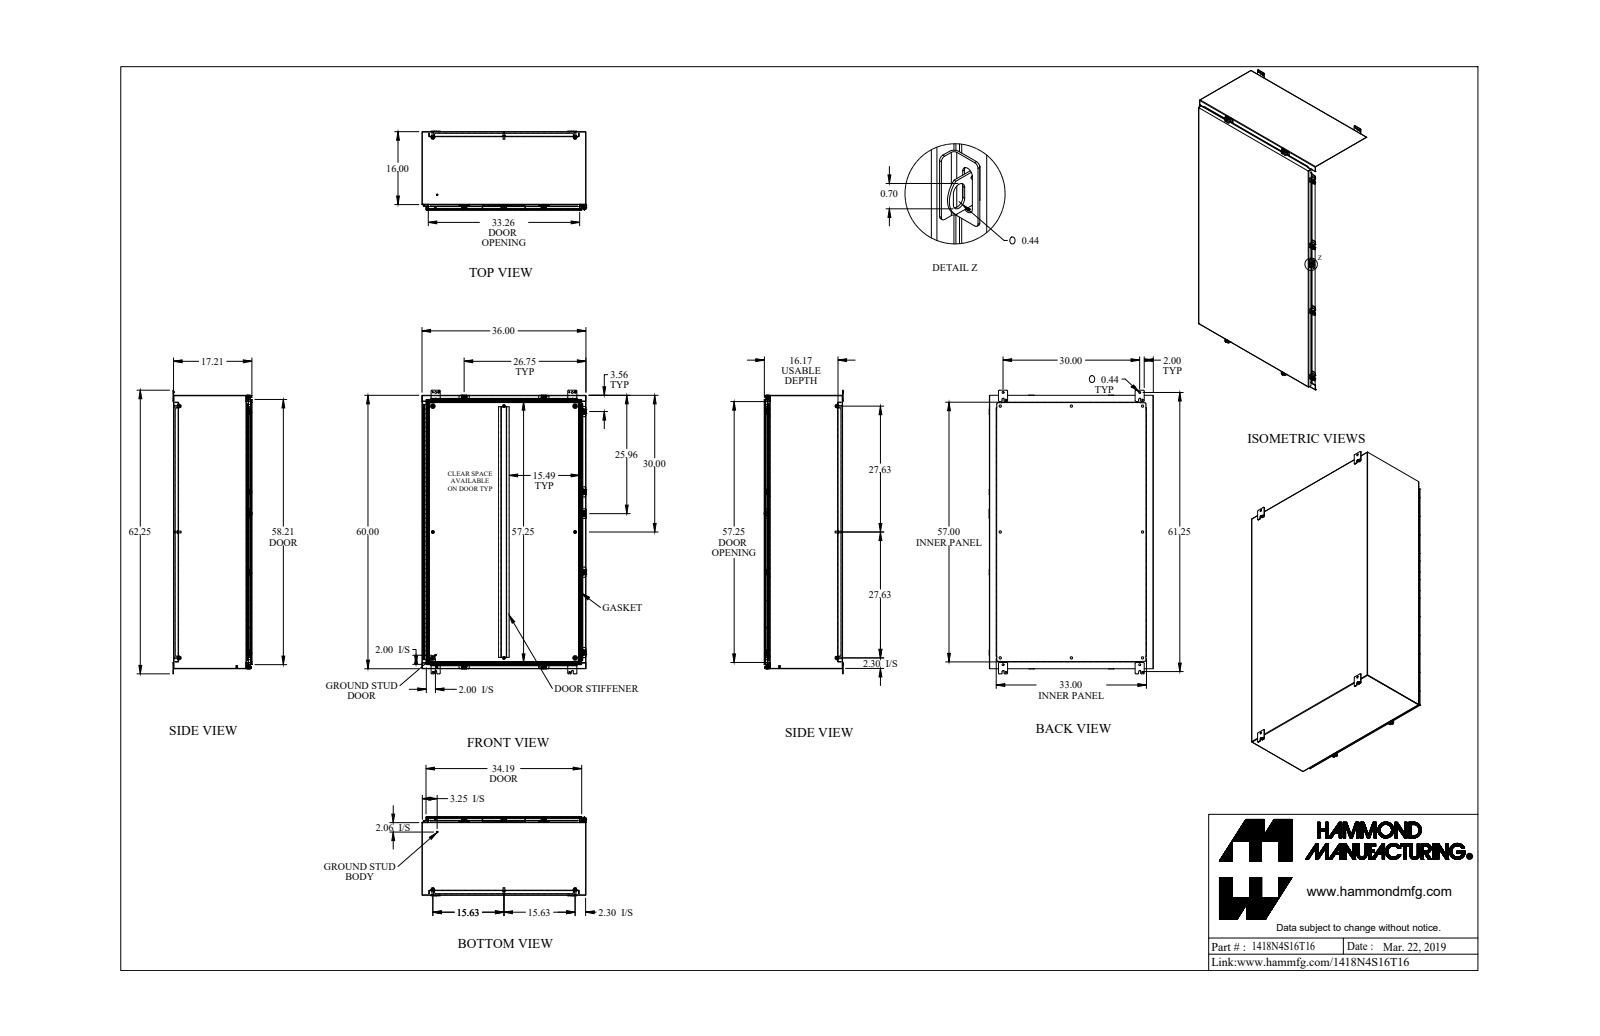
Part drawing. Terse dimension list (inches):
name: 1418N4S16T16
written by: SolidWorks 2019 (AUTOMOTIVE_DESIGN)
unit: in
bodies: 64 solids, 1724 faces (1010 planar, 624 cylindrical, 90 other)
size: 62.25 × 36.063 × 17.375
volume: 796.5 in³; area: 20 868 in²
holes: 8× ⌀0.213, 8× ⌀0.265, 8× ⌀0.375, 8× ⌀0.5, 4× ⌀0.307, 4× ⌀0.313, 4× ⌀0.445, 2× ⌀0.437, 1× ⌀0.11, 1× ⌀0.125
bosses: 8× ⌀0.65, 8× ⌀0.5, 8× ⌀0.39, 8× ⌀0.375, 8× ⌀0.332, 8× ⌀0.244, 4× ⌀1, 2× ⌀0.313
rounds: 44× R0.25, 39× R0.048, 39× R0.143, 30× R0.188, 22× R0.036, 22× R0.108, 16× R0.141, 14× R0.125
face distances: 0.072, 17.066, 17.138, 0.072, 0.095, 17.138, 17.21, 0.937, 1.009, 35.928
hole spacings: 27.625, 31.25, 62.338, 63.475, 7.196, 9.004, 15.625, 24.468
